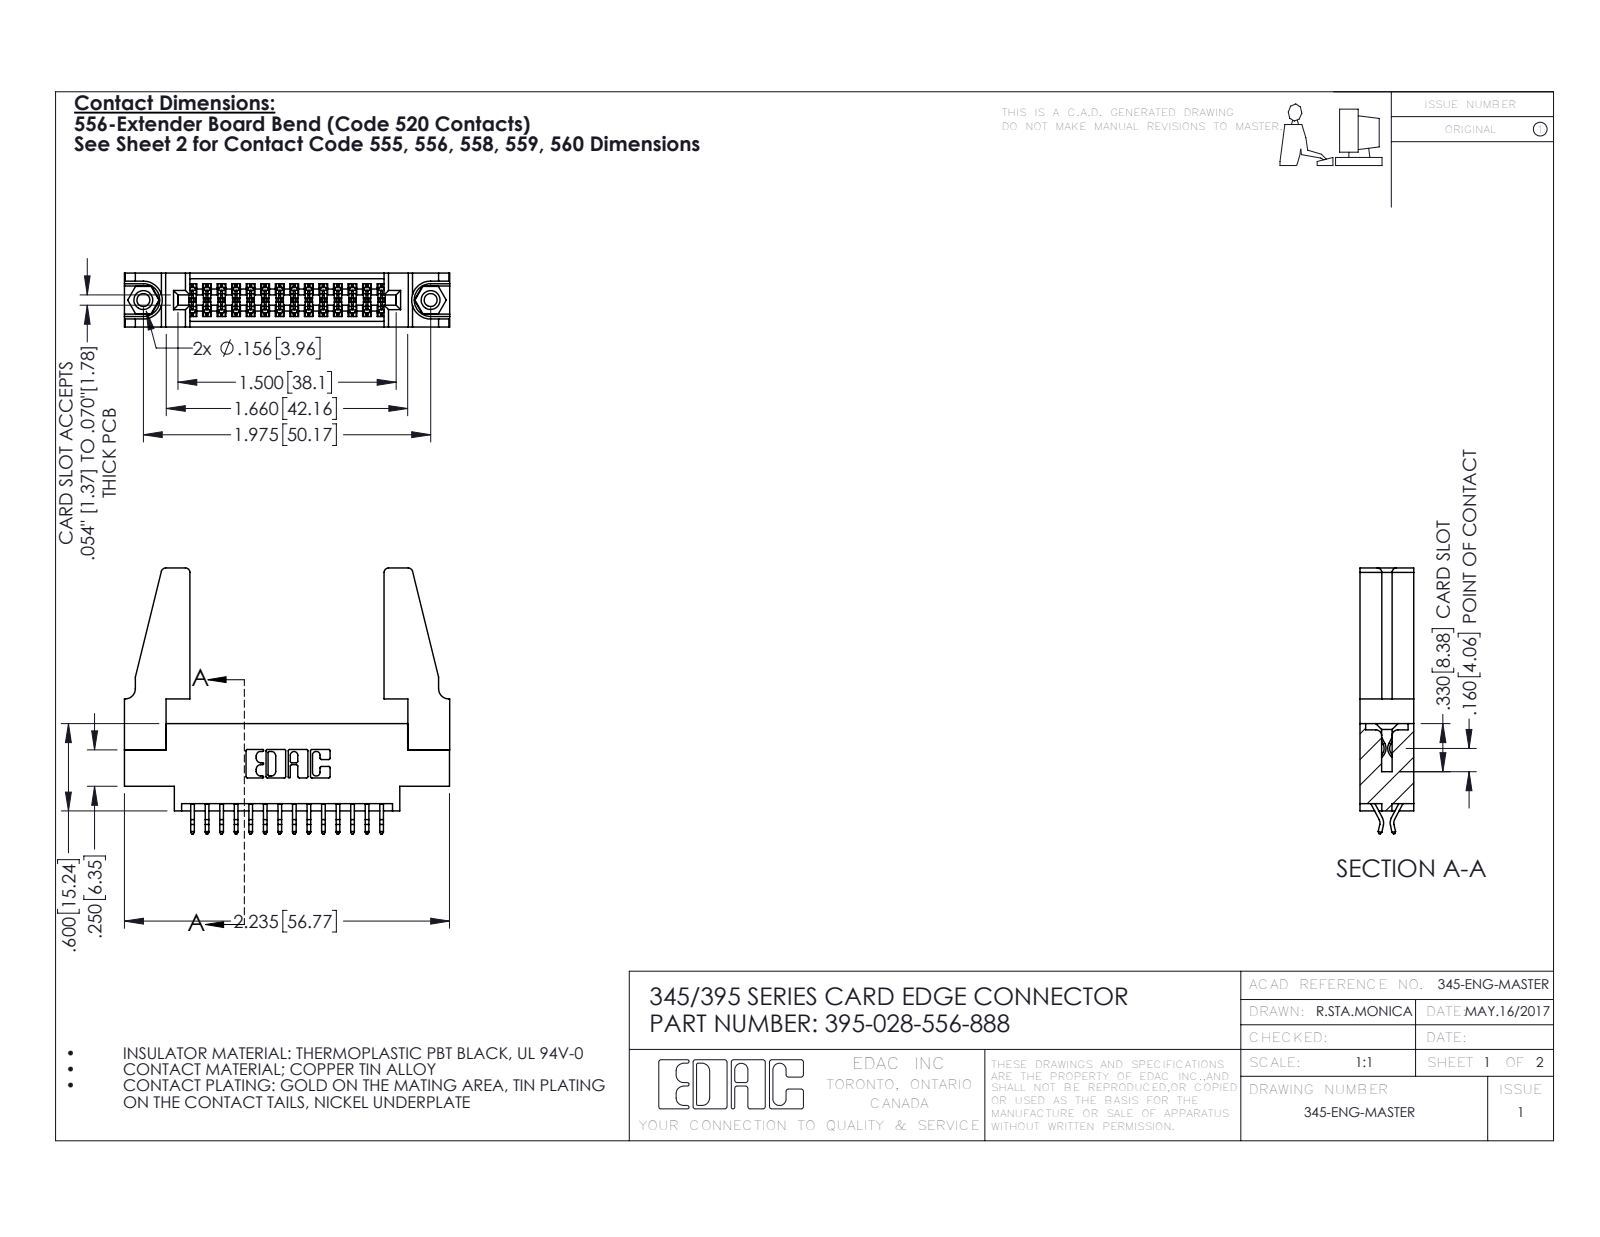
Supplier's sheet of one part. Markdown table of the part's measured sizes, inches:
| quantity | value |
| --- | --- |
| part name | 395-028-556-888; 345-292-001_556 Tail; 345-250-001_345-250-001-102; 345 Part_0.170 Offset - 0.156 Dia-TH (+1 more) |
| STEP written by | SolidWorks 2016 (CONFIG_CONTROL_DESIGN) |
| units | inches |
| bodies | 33 solids, 1822 faces (1192 planar, 614 cylindrical, 16 other) |
| overall size | 2.236 × 1.827 × 0.37 |
| volume | 0.512 in³ |
| surface area | 15.97 in² |
| round holes (diameter × count) | 0.089 × 2, 0.125 × 2, 0.156 × 2, 0.064 × 1 |
| round bosses / shafts (diameter × count) | 0.155 × 2 |
| partial cylindrical surfaces (radius × count) | 0.006 × 42, 0.01 × 22, 0.03 × 8, 0.007 × 6, 0.031 × 6, 0.026 × 3, 0.01 × 2, 0.014 × 2 |
| main face-to-face distances | 0.37, 0.072, 0.298, 0.2, 0.025, 0.098, 0.272, 0.225, 0.175, 0.148 |
| hole center spacings | 0.27, 1.742, 1.975 |
